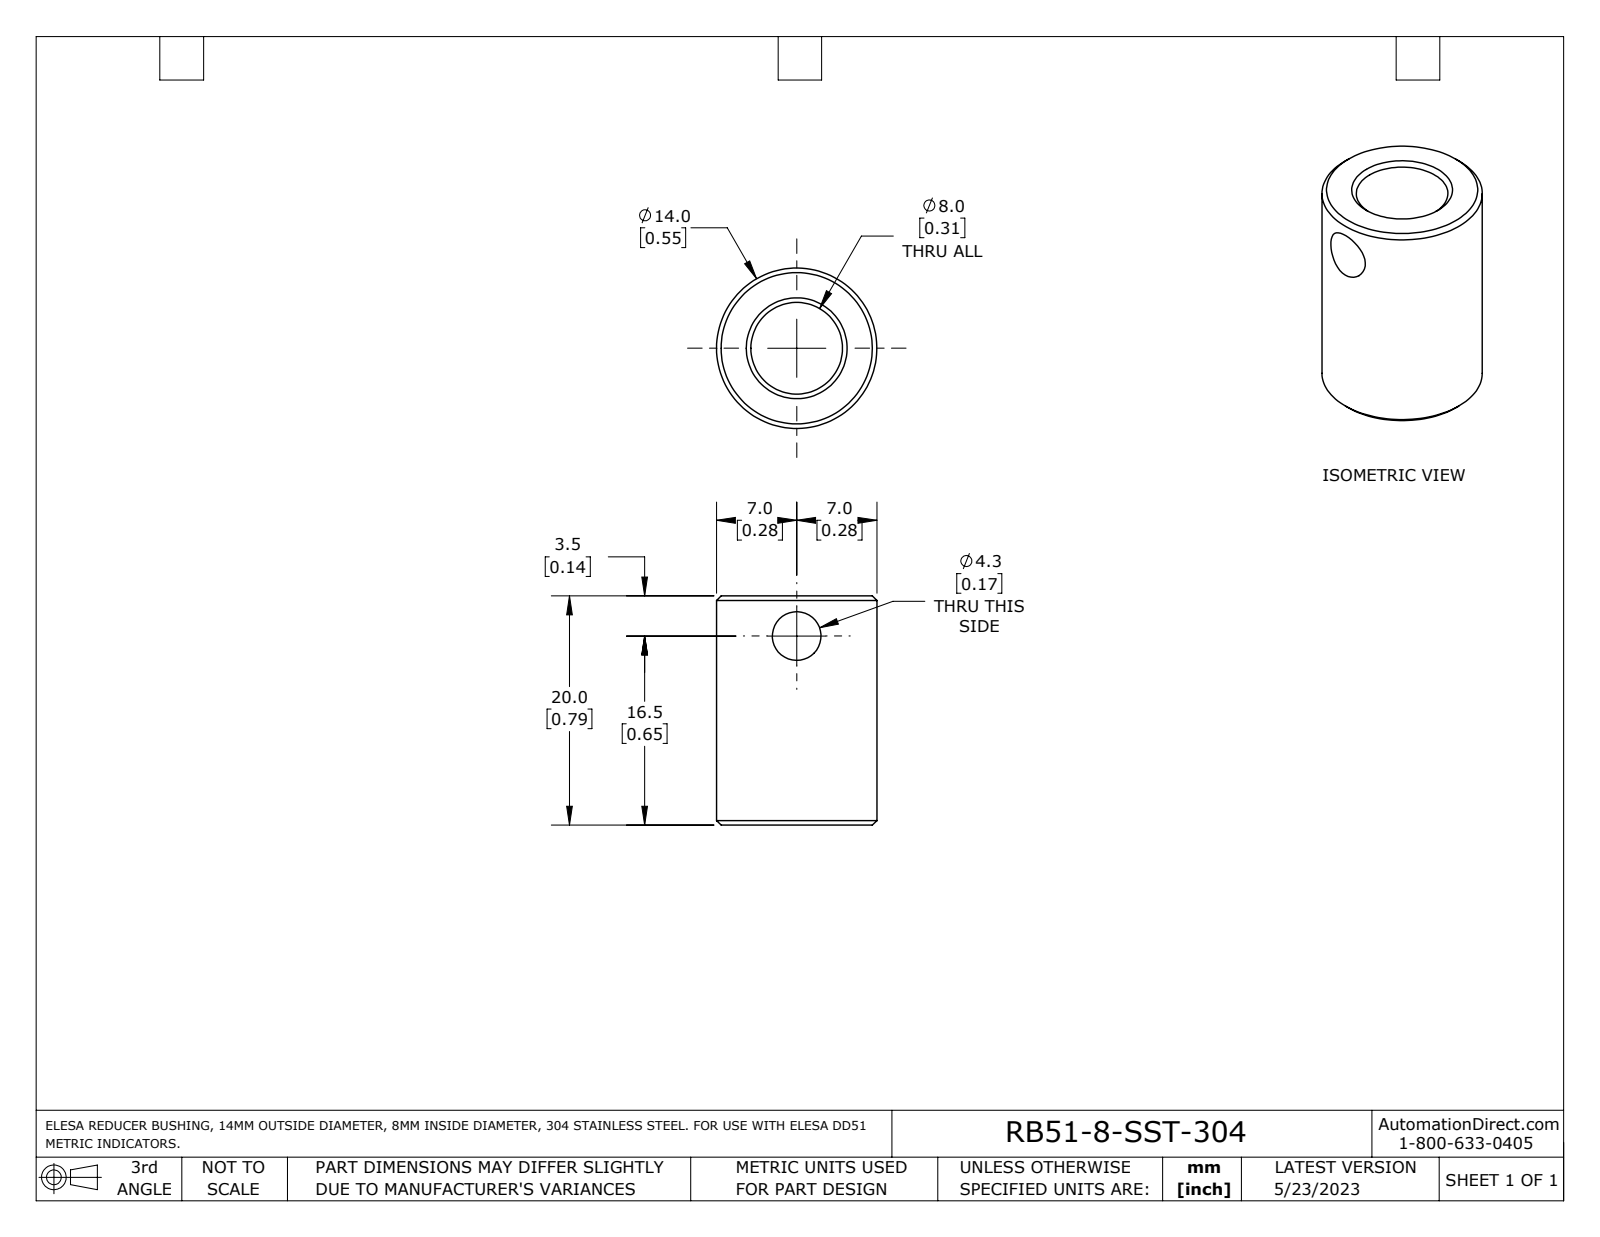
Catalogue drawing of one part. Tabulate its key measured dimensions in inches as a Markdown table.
| quantity | value |
| --- | --- |
| part name | RB51-8-SST-304 |
| STEP written by | SolidWorks 2021 (AUTOMOTIVE_DESIGN) |
| units | inches |
| bodies | 1 solid, 9 faces (2 planar, 3 cylindrical, 4 other) |
| overall size | 0.787 × 0.551 × 0.551 |
| volume | 0.123 in³ |
| surface area | 2.434 in² |
| round holes (diameter × count) | 0.167 × 1, 0.315 × 1 |
| round bosses / shafts (diameter × count) | 0.551 × 1 |
| main face-to-face distances | 0.787 |
